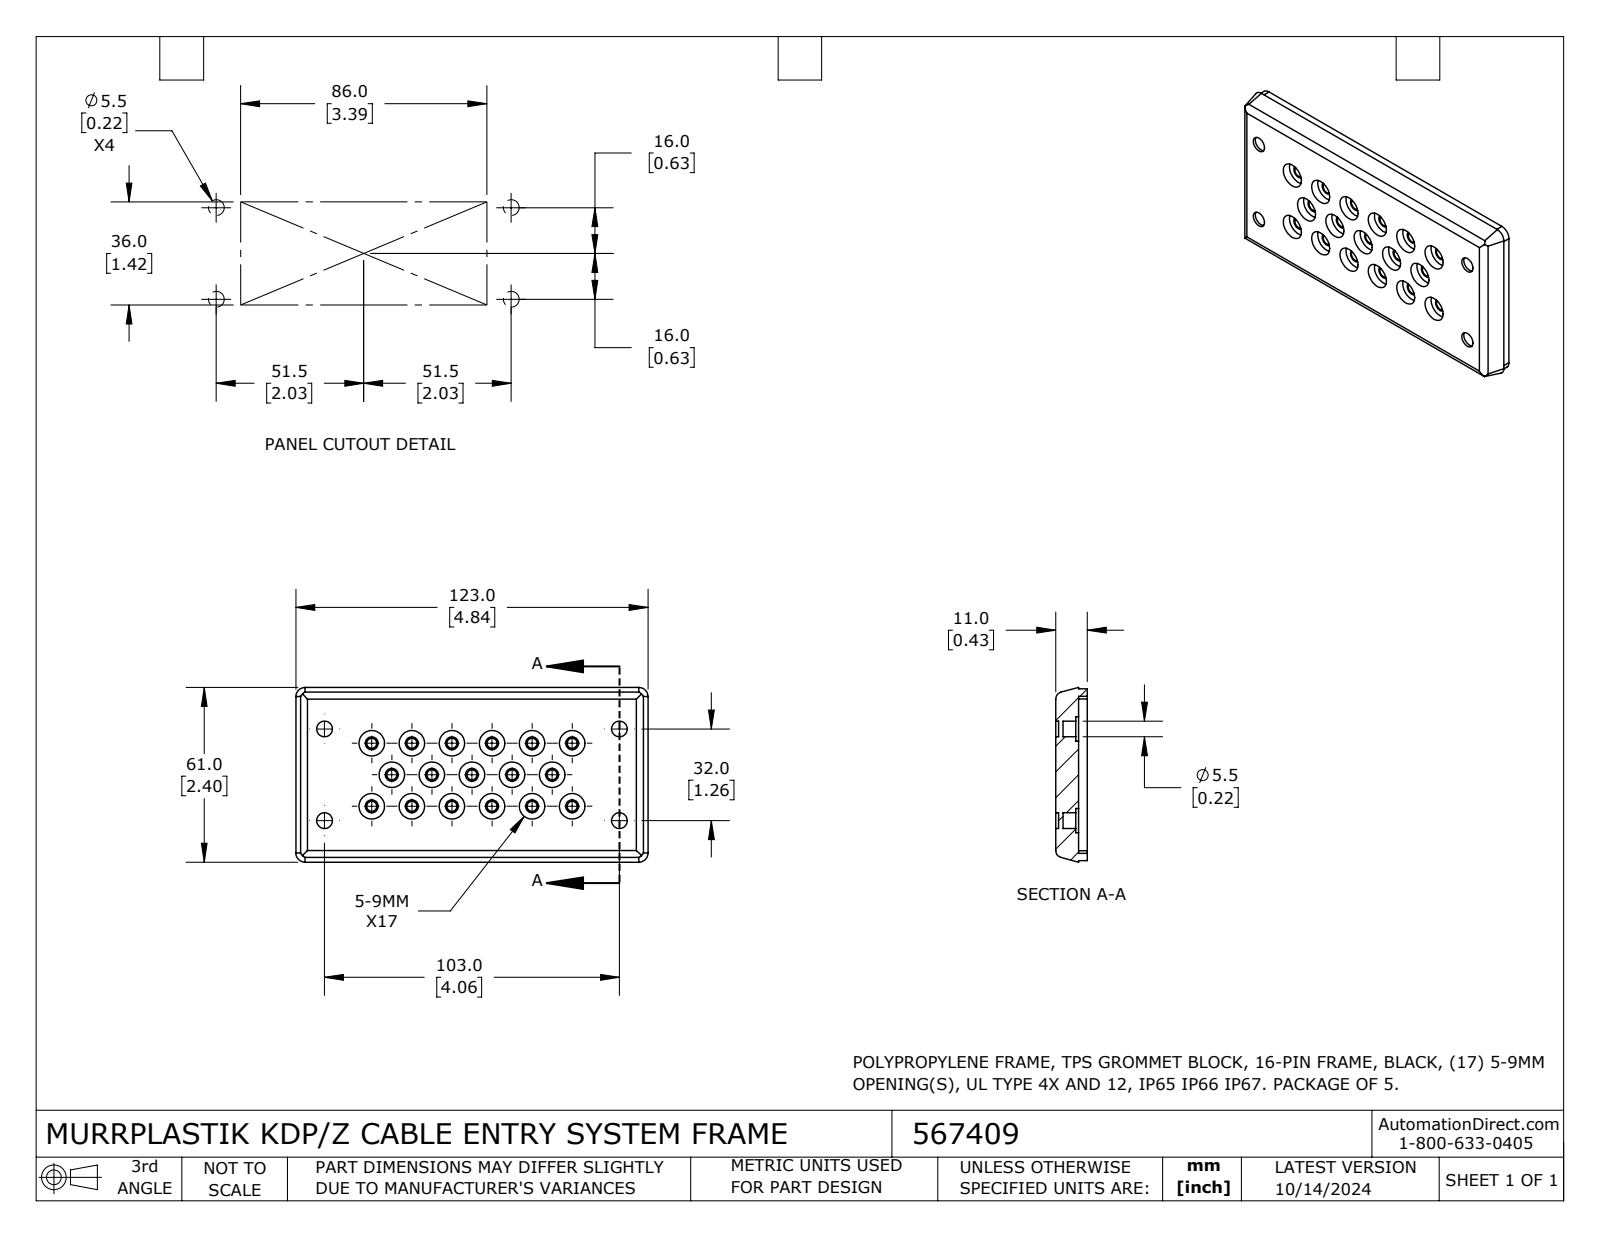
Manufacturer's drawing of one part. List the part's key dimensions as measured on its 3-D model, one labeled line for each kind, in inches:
Part name (STEP PRODUCT): 567409
STEP written by: SolidWorks 2023 (CONFIG_CONTROL_DESIGN)
Units: inches
Bodies: 1 solid, 253 faces (93 planar, 156 cylindrical, 4 other)
Overall size (bounding box): 4.843 × 2.402 × 0.433
Volume: 2.731 in³ · Surface area: 37.05 in²
Round holes (diameter × count): ⌀0.177 ×17, ⌀0.35 ×17, ⌀0.217 ×4, ⌀0.335 ×4
Round bosses / shafts (diameter × count): ⌀0.138 ×17
Partial cylindrical surfaces — rounded edges, fillets, slot ends (radius × count): R0.012 ×8, R0.035 ×4, R0.098 ×4, R0.138 ×4, R0.244 ×4, R0.266 ×4
Main face-to-face distances: 0.217, 0.098, 0.315, 0.118, 0.433, 0.197, 0.102, 0.386, 1.976, 2.26
Hole centre spacings: 0.513, 0.933, 0.551, 1.444, 1.102, 1.027, 1.402, 1.654
